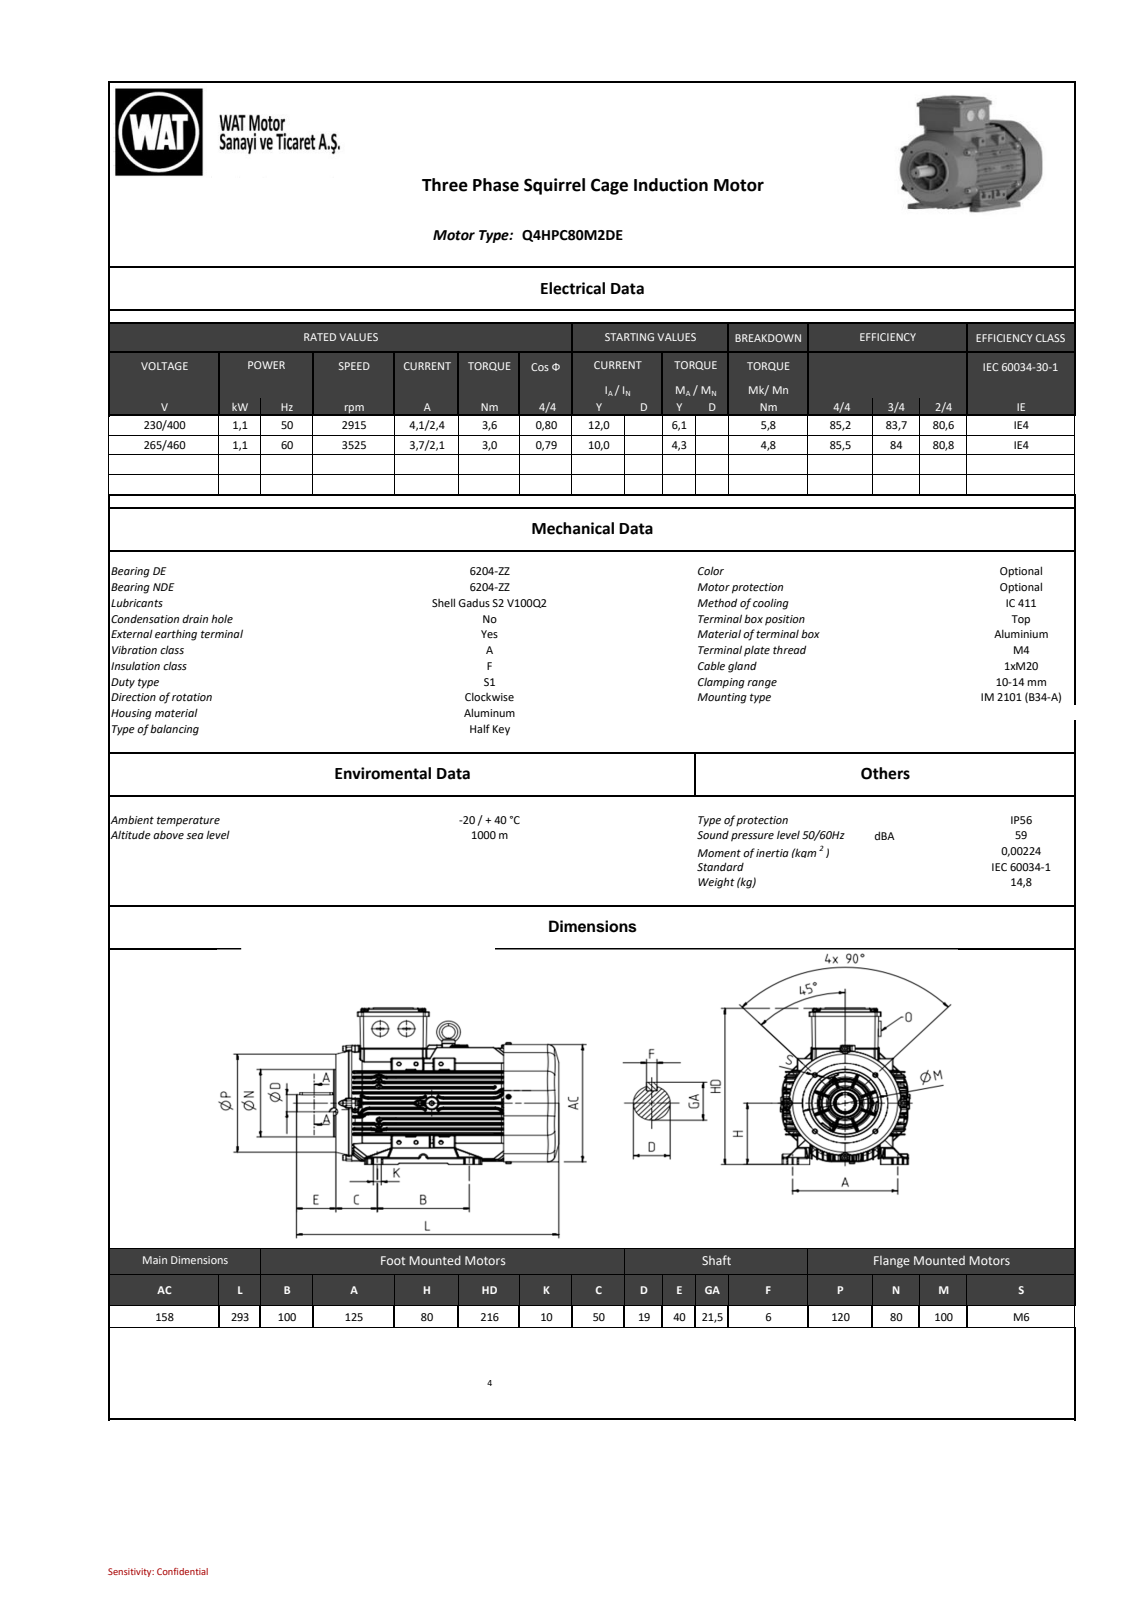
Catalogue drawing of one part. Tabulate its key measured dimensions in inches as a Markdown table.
| quantity | value |
| --- | --- |
| part name | model1 |
| STEP written by | SIEMENS PLM Software NX2206.8101 (AUTOMOTIVE_DESIGN) |
| units | inches |
| bodies | 0 solids, 5799 faces (1188 planar, 1735 cylindrical, 2876 other) |
| overall size | 11.535 × 8.484 × 6.22 |
| round holes (diameter × count) | 0.118 × 3, 0.138 × 2, 0.181 × 2, 0.197 × 2, 0.13 × 1, 0.315 × 1, 2.244 × 1 |
| round bosses / shafts (diameter × count) | 0.236 × 5, 0.328 × 3, 0.842 × 2, 5.768 × 1, 3.15 × 1, 2.402 × 1, 1.181 × 1, 0.948 × 1 |
| partial cylindrical surfaces (radius × count) | 0.02 × 602, 0.031 × 283, 0.039 × 266, 0.079 × 23, 0.197 × 16, 2.982 × 8, 0.089 × 4, 0.118 × 4 |
| main face-to-face distances | 0.039, 1.652, 0.408, 6.181, 6.18, 3.386, 0.709, 2.06, 8.701, 0.413 |
| hole center spacings | 1.004, 1.739, 1.739, 1.98, 2.144, 2.793 |
